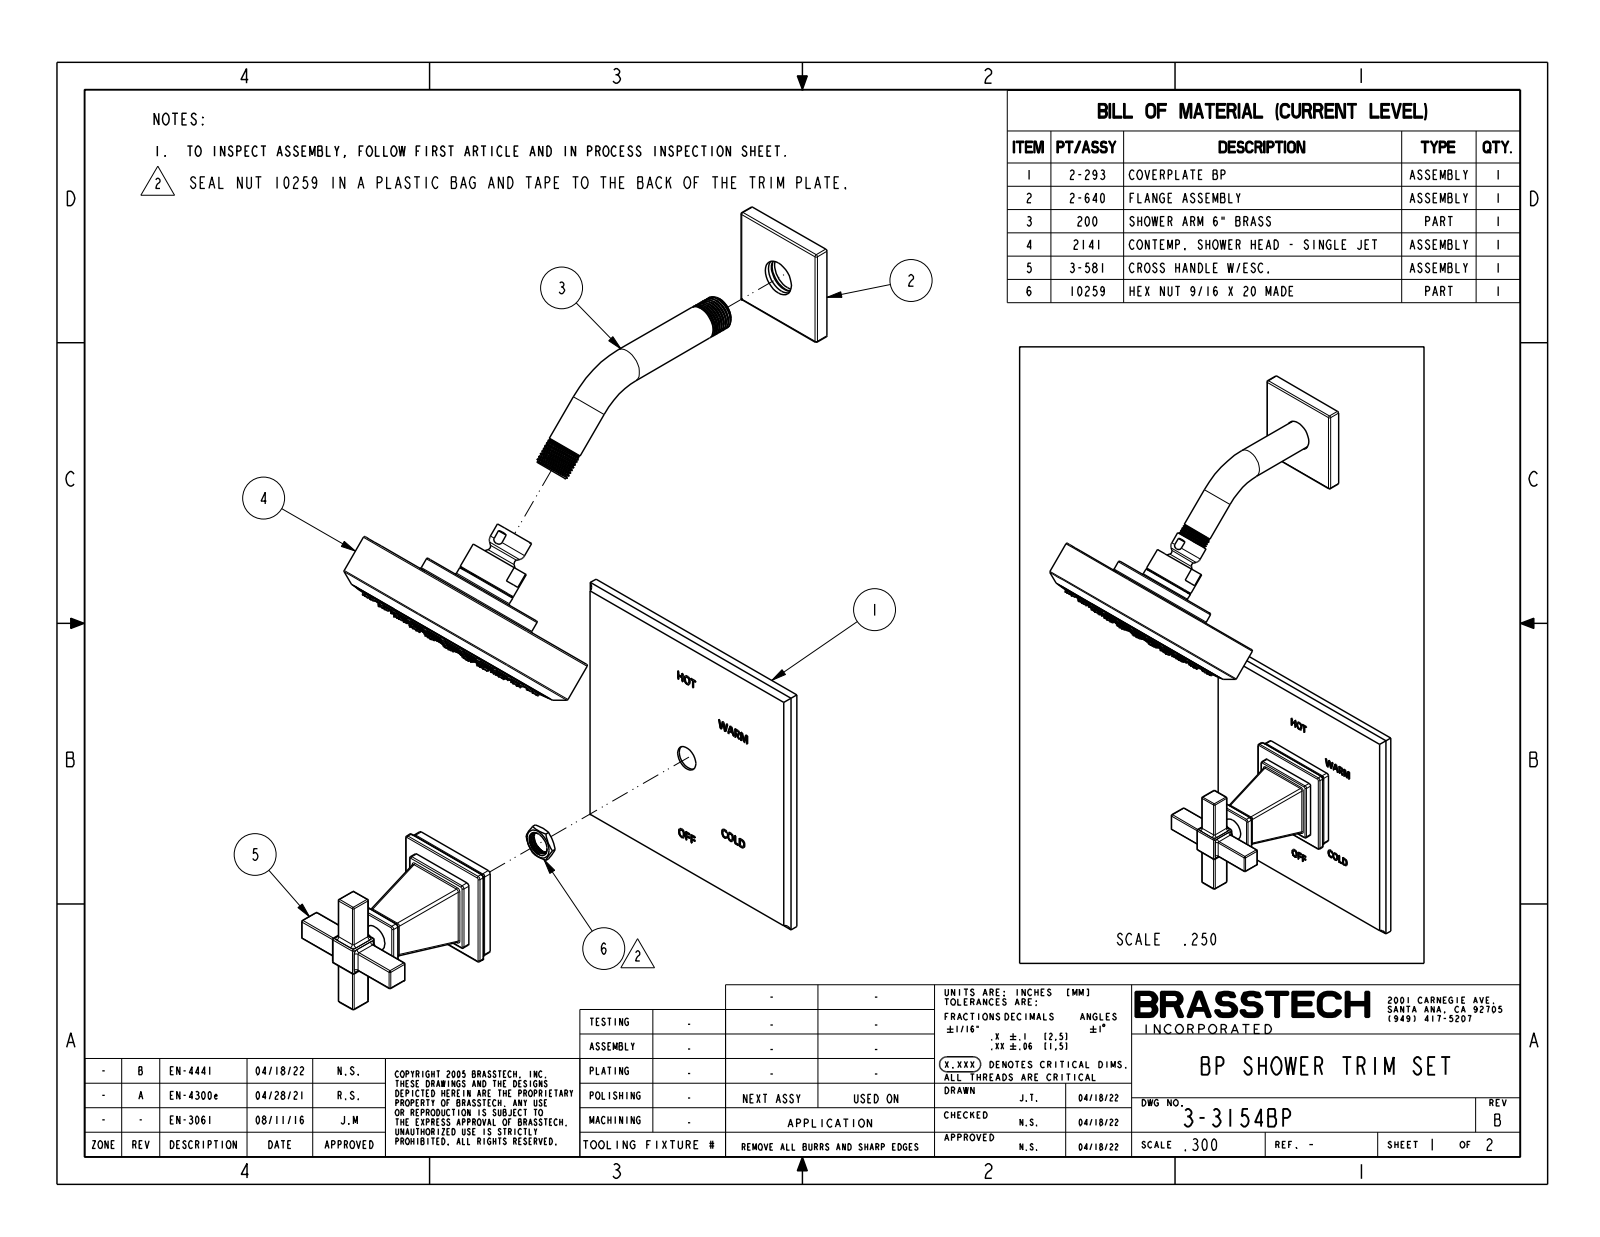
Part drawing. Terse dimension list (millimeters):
name: 3-3154BP
written by: CREO PARAMETRIC BY PTC INC, 2018400 (CONFIG_CONTROL_DESIGN)
unit: mm
bodies: 2 solids, 1373 faces (295 planar, 345 cylindrical, 733 other)
size: 418.5 × 215.5 × 165.1
volume: 965 400 mm³; area: 149 700 mm²
holes: 90× ⌀1.3, 1× ⌀5.6, 1× ⌀133.5
bosses: 2× ⌀35.6, 2× ⌀20.7, 1× ⌀150.1, 1× ⌀132.6, 1× ⌀74.2, 1× ⌀23, 1× ⌀19.5, 1× ⌀15.9
rounds: 60× R0.8, 36× R1.5, 8× R1, 8× R2.3, 4× R3.2, 4× R5.8
face distances: 8, 8.9, 0.9, 7.4, 12.7, 76.2, 88.9, 18.4, 10.4, 9.5
hole spacings: 24.9, 35.8, 10.9, 14, 34.1, 48.1, 14.6, 21.6
